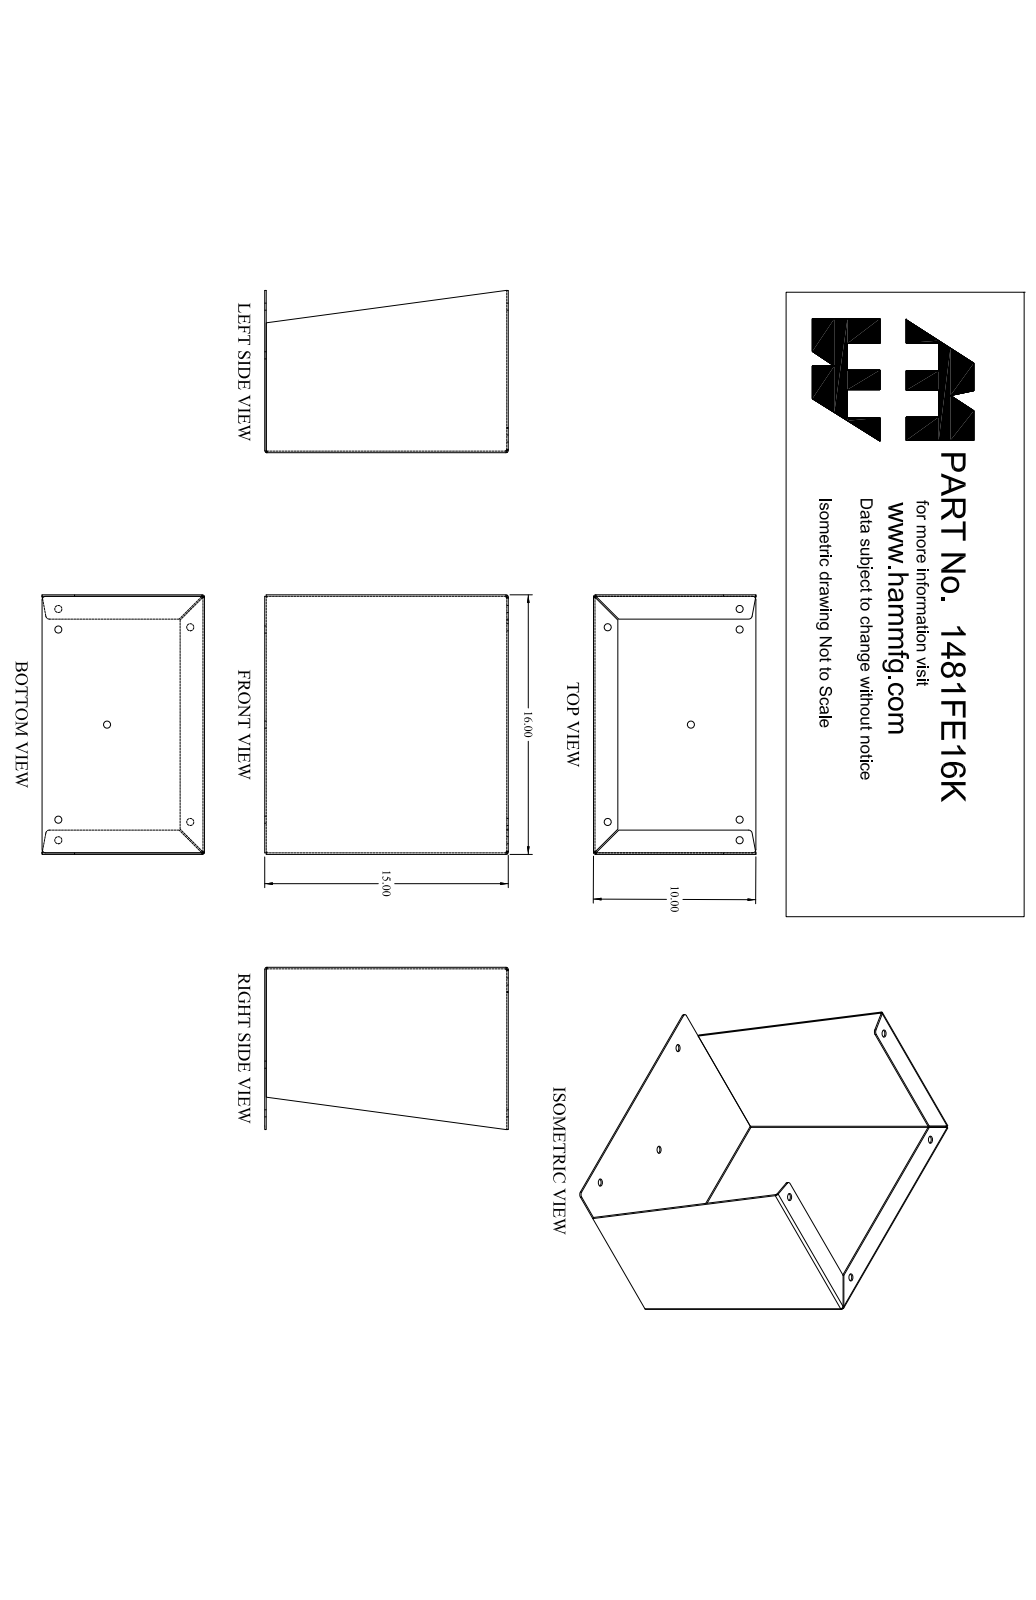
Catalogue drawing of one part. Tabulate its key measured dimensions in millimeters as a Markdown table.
| quantity | value |
| --- | --- |
| part name | 1481FE16K_Default |
| STEP written by | SolidWorks 2019 (CONFIG_CONTROL_DESIGN) |
| units | millimeters |
| bodies | 1 solid, 78 faces (42 planar, 30 cylindrical, 6 other) |
| overall size | 406.4 × 381 × 254 |
| volume | 1 095 000 mm³ |
| surface area | 915 500 mm² |
| round holes (diameter × count) | 11.1 × 7 |
| partial cylindrical surfaces (radius × count) | 1.2 × 6, 3.6 × 6, 5.6 × 4 |
| main face-to-face distances | 2.4, 404, 2.4, 406.4, 401.6, 376.2, 378.6, 378.6, 381, 35.7 |
| hole center spacings | 167.2, 200.4, 206.4, 208.3, 365.1, 32.2, 32.2, 196.4 |
